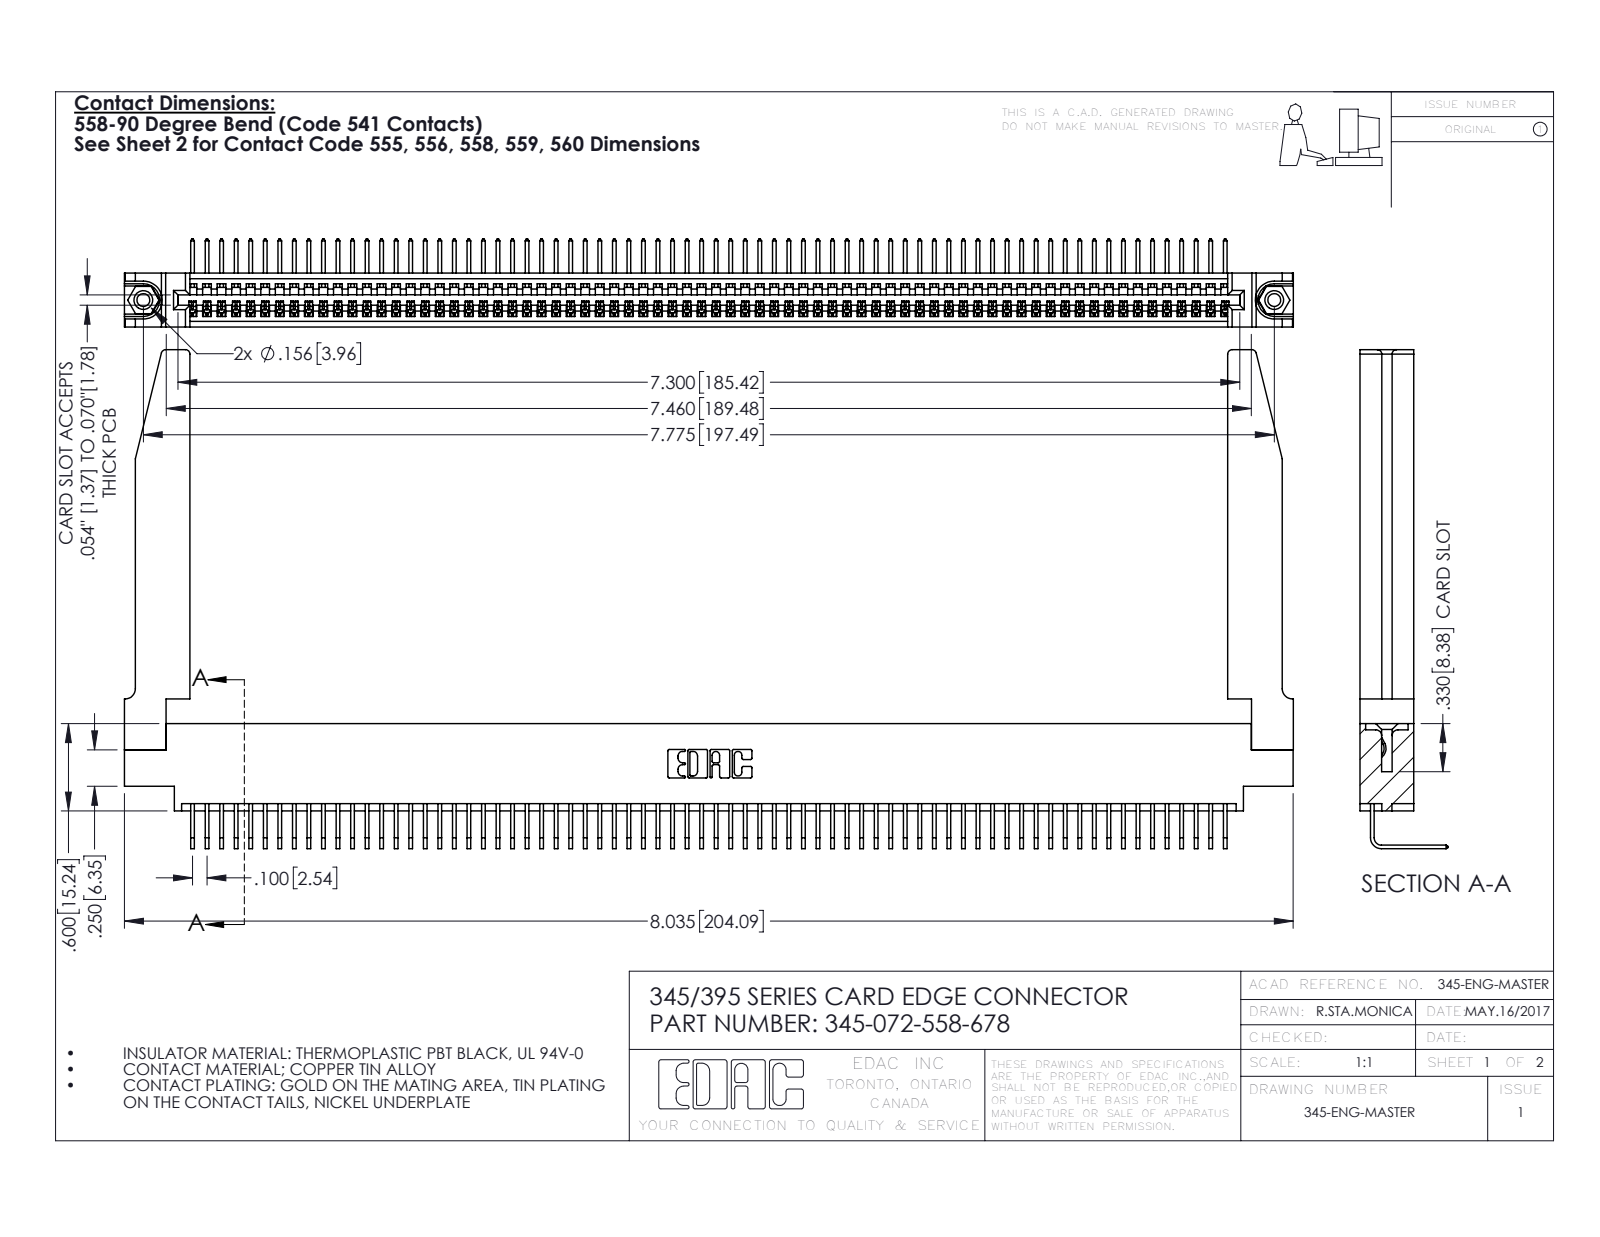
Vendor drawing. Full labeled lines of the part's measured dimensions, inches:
Part name (STEP PRODUCT): 345-072-558-678; 345-292-001_558 Tail - 2; 345-250-001_345-250-001-102; 345 Part_0.170 Offset - 0.156 Dia-TH (+1 more)
STEP written by: SolidWorks 2016 (CONFIG_CONTROL_DESIGN)
Units: inches
Bodies: 77 solids, 4684 faces (3250 planar, 1382 cylindrical, 52 other)
Overall size (bounding box): 8.036 × 3.429 × 0.605
Volume: 1.68 in³ · Surface area: 54.32 in²
Round holes (diameter × count): ⌀0.089 ×2, ⌀0.125 ×2, ⌀0.156 ×2, ⌀0.064 ×1
Round bosses / shafts (diameter × count): ⌀0.155 ×2
Partial cylindrical surfaces — rounded edges, fillets, slot ends (radius × count): R0.006 ×144, R0.01 ×22, R0.03 ×8, R0.007 ×6, R0.031 ×6, R0.026 ×3, R0.031 ×2, R0.04 ×2
Main face-to-face distances: 0.072, 0.37, 0.298, 0.098, 0.272, 0.025, 0.2, 0.225, 0.149, 0.175
Hole centre spacings: 0.27, 7.539, 7.775
